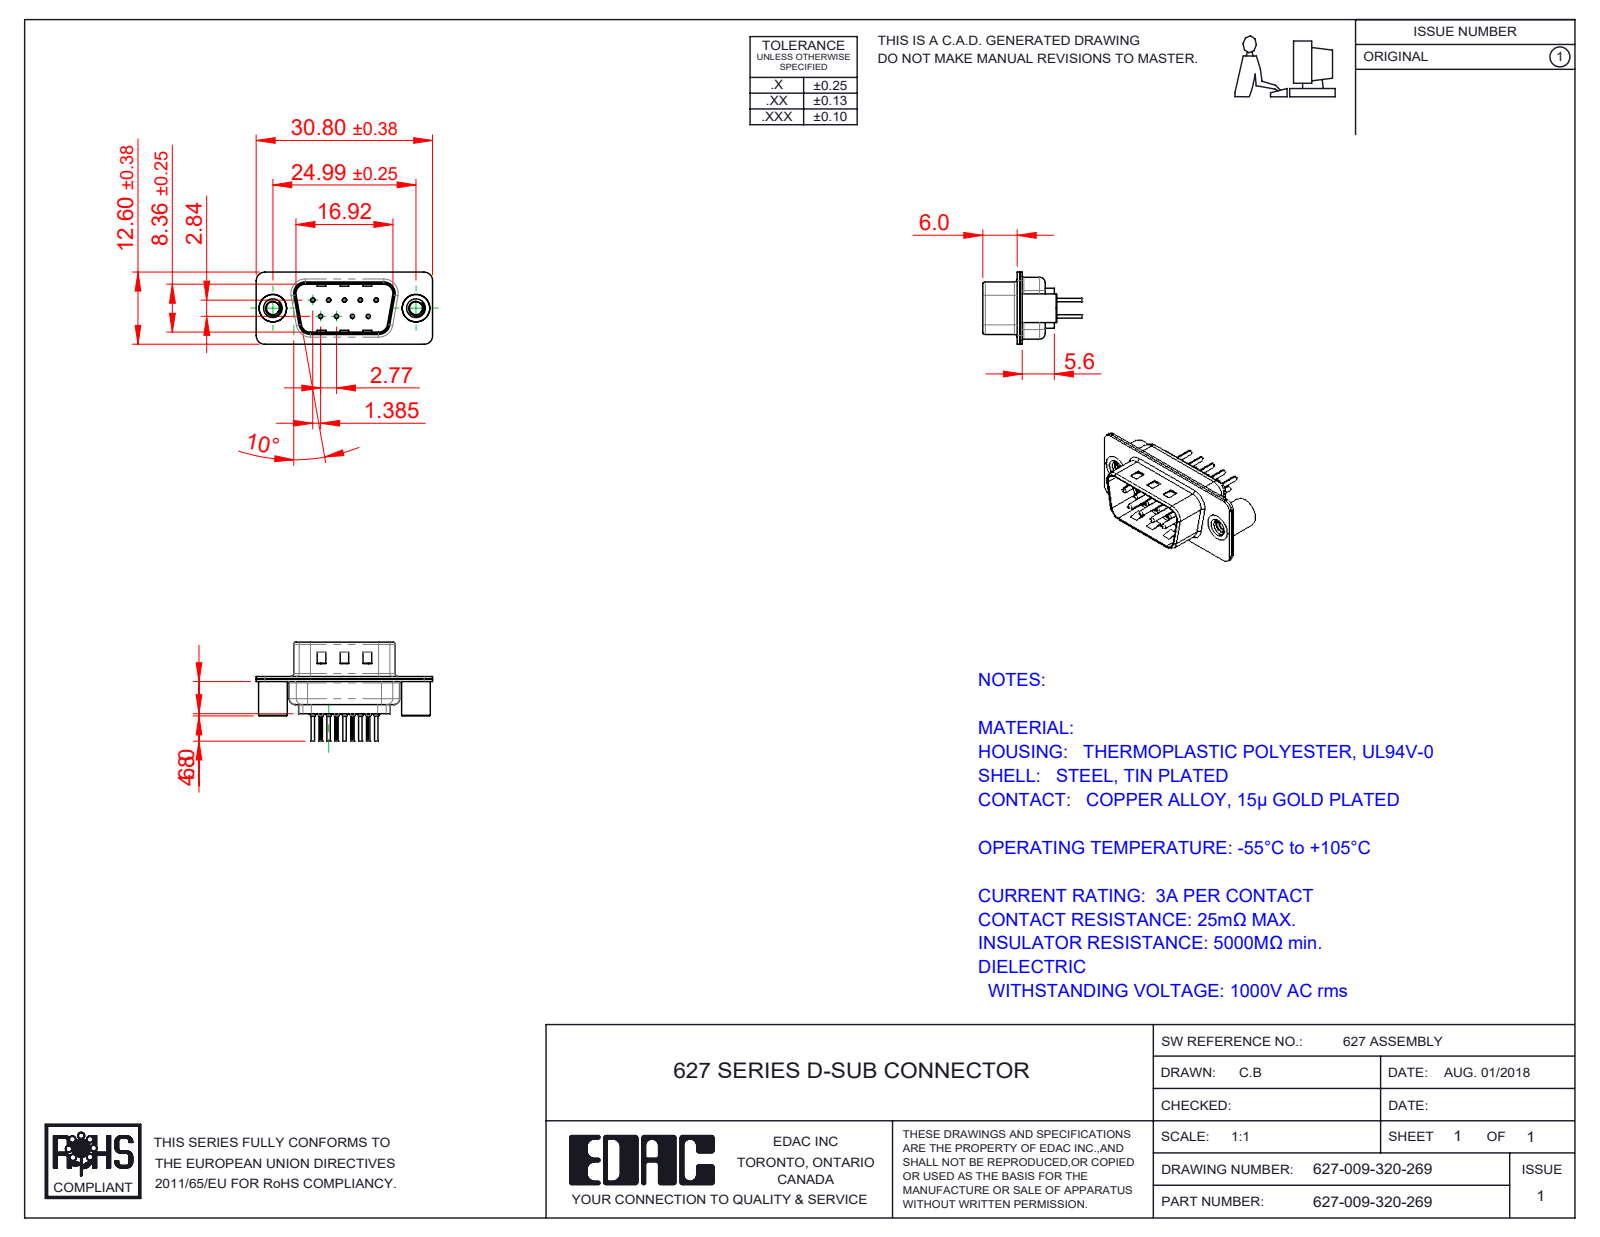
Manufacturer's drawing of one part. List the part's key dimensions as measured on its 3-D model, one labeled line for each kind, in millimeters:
Part name (STEP PRODUCT): 627 Contact Row 2_20L; 627 Contact Row 1_20L; 627 Housing_09 LP; 627-009-320-069 (+3 more)
STEP written by: SolidWorks 2020 (CONFIG_CONTROL_DESIGN)
Units: millimetres
Bodies: 14 solids, 1208 faces (323 planar, 482 cylindrical, 403 other)
Overall size (bounding box): 30.8 × 17.3 × 12.6
Volume: 1 408 mm³ · Surface area: 4 125 mm²
Round holes (diameter × count): ⌀0.2 ×9, ⌀0.35 ×9, ⌀1.1 ×9, ⌀1.6 ×9, ⌀2.26 ×2, ⌀4 ×2, ⌀4.8 ×2
Round bosses / shafts (diameter × count): ⌀2 ×9, ⌀1.5 ×9, ⌀0.75 ×9, ⌀0.6 ×9, ⌀5 ×2, ⌀4.9 ×2
Partial cylindrical surfaces — rounded edges, fillets, slot ends (radius × count): R0.1 ×18, R1.5 ×18, R2 ×12, R0.5 ×8, R1.6 ×8, R0.25 ×4, R0.6 ×4, R0.65 ×4
Main face-to-face distances: 0.45, 0.4, 0.9, 0.82, 9.58, 1.4, 8.76, 6.5, 0.5, 1.5
Hole centre spacings: 3.16, 2.77, 5.54, 5.03, 5.04, 8.31, 7.48, 7.49
